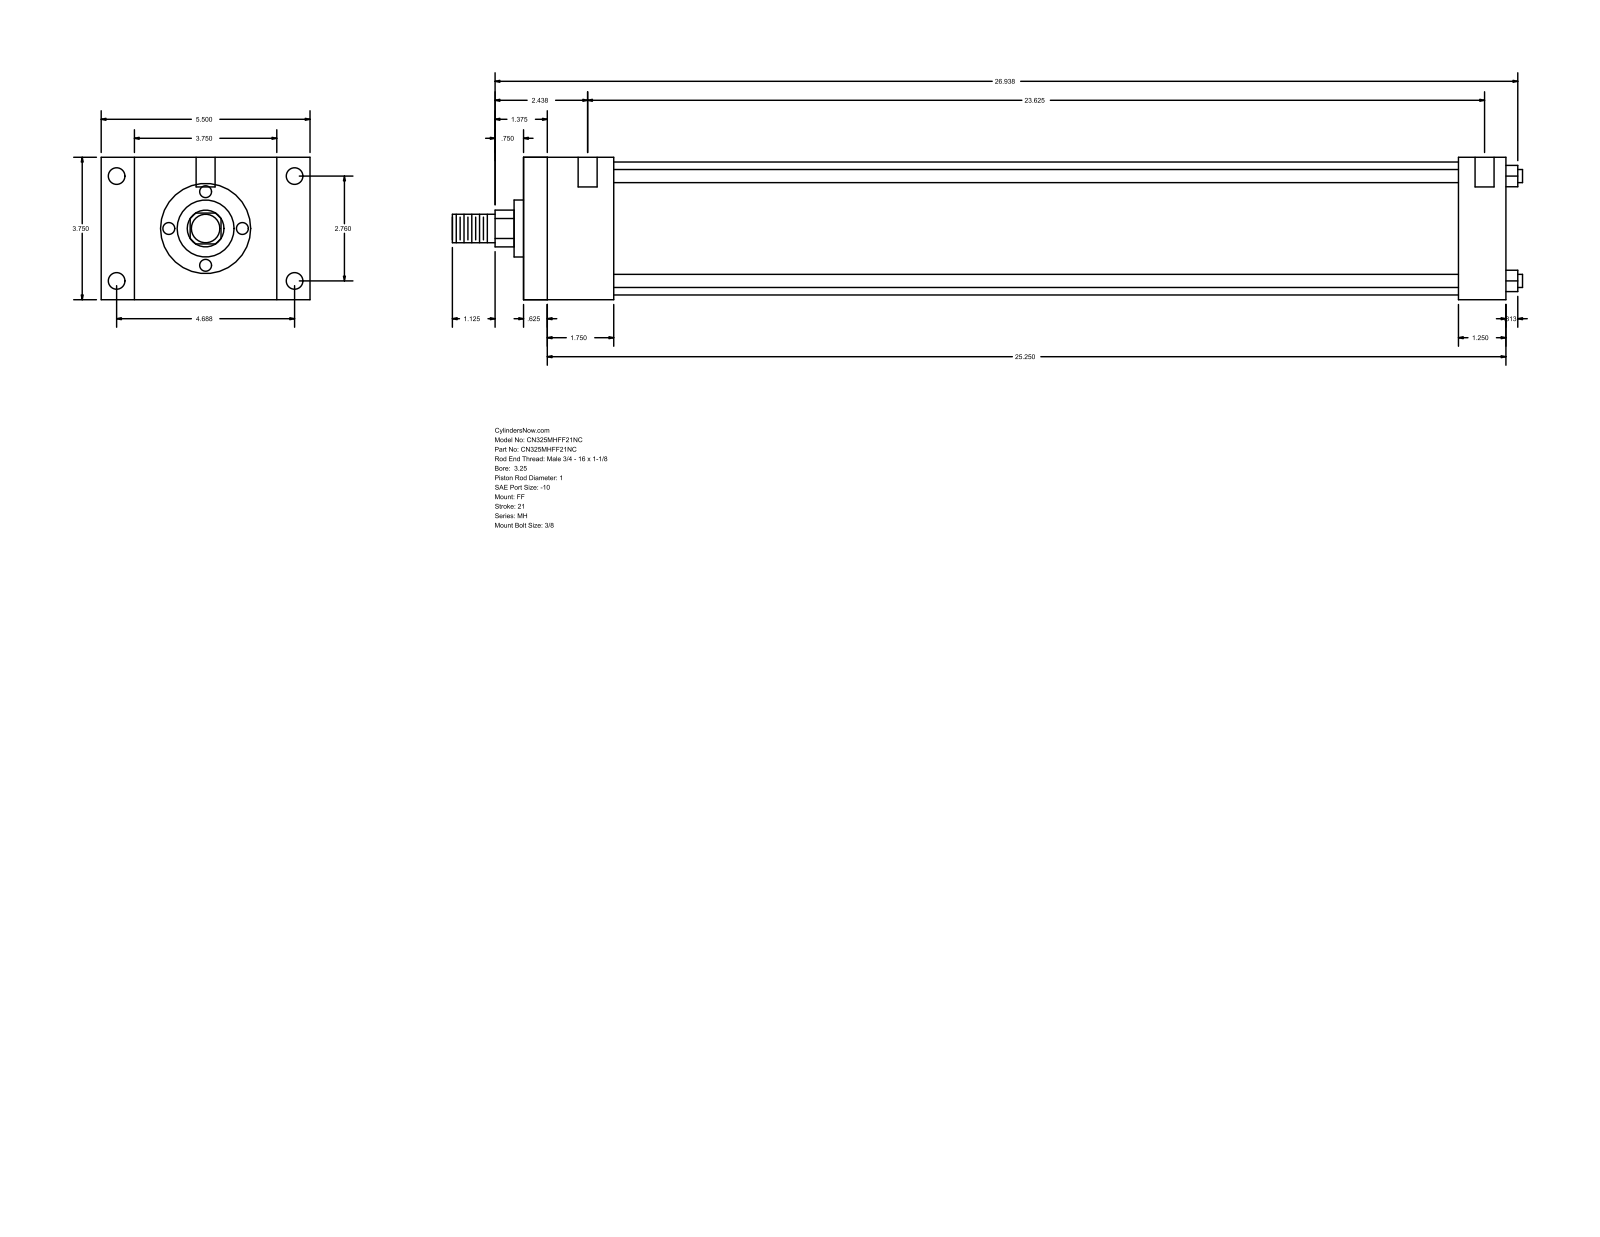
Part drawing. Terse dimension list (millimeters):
name: MH_FF__0325_1
written by: GSSL Pune (CONFIG_CONTROL_DESIGN)
unit: mm
bodies: 0 solids, 92 faces (64 planar, 28 cylindrical, 0 other)
size: 715.96 × 139.7 × 95.25
holes: 4× ⌀5.56, 4× ⌀11.13, 2× ⌀12.7
bosses: 4× ⌀8.76, 1× ⌀88.9, 1× ⌀38.1, 1× ⌀25.4, 1× ⌀19.05
rounds: 1× R12.29
face distances: 95.24, 657.22, 15.87, 641.35, 22.23, 117.47, 625.47, 609.6, 31.75, 60.33
hole spacings: 70.1, 119.06, 138.16, 606.42, 1.58, 4.76, 600.08, 601.66
